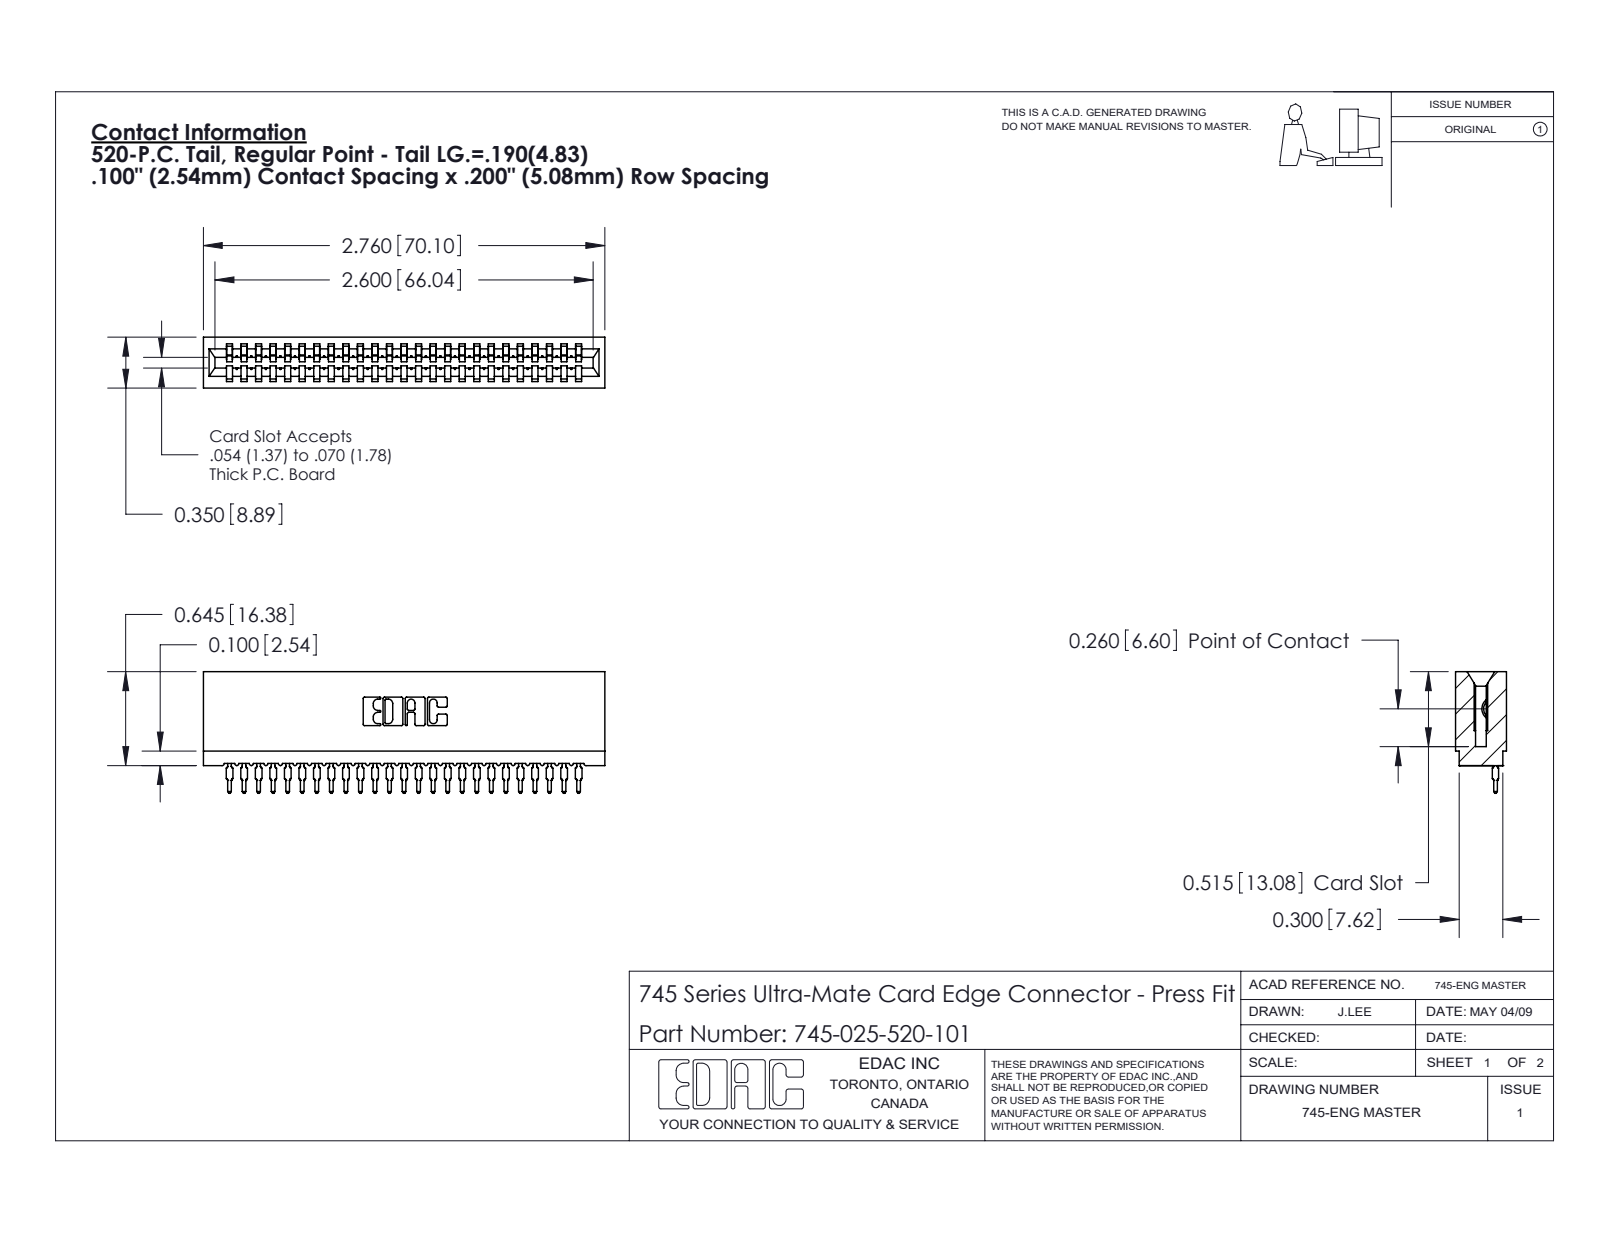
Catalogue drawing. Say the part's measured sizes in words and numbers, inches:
The part is named "745 Part_Insulator Option - 01; 745-292-001_520; 745-025-520-101". Its 3-D file was written by "SolidWorks 2020 (CONFIG_CONTROL_DESIGN)". It is 26 solids with 2895 faces: 1730 planar, 515 cylindrical and 650 other. Overall it measures 2.76 by 0.836 by 0.35 inches. Its volume is 0.375 cubic inches and its surface area 17.02 square inches. Partial cylindrical surfaces (rounded edges, fillets, slot ends): 50 of radius 0.015, 50 of radius 0.021, 22 of radius 0.01, 6 of radius 0.007, 6 of radius 0.031, 4 of radius 0.005, 4 of radius 0.011, 3 of radius 0.026. The main face-to-face distances are 0.1, 0.2, 0.35, 0.138, 0.212, 0.045, 0.305, 0.093, 0.167, 0.3.
